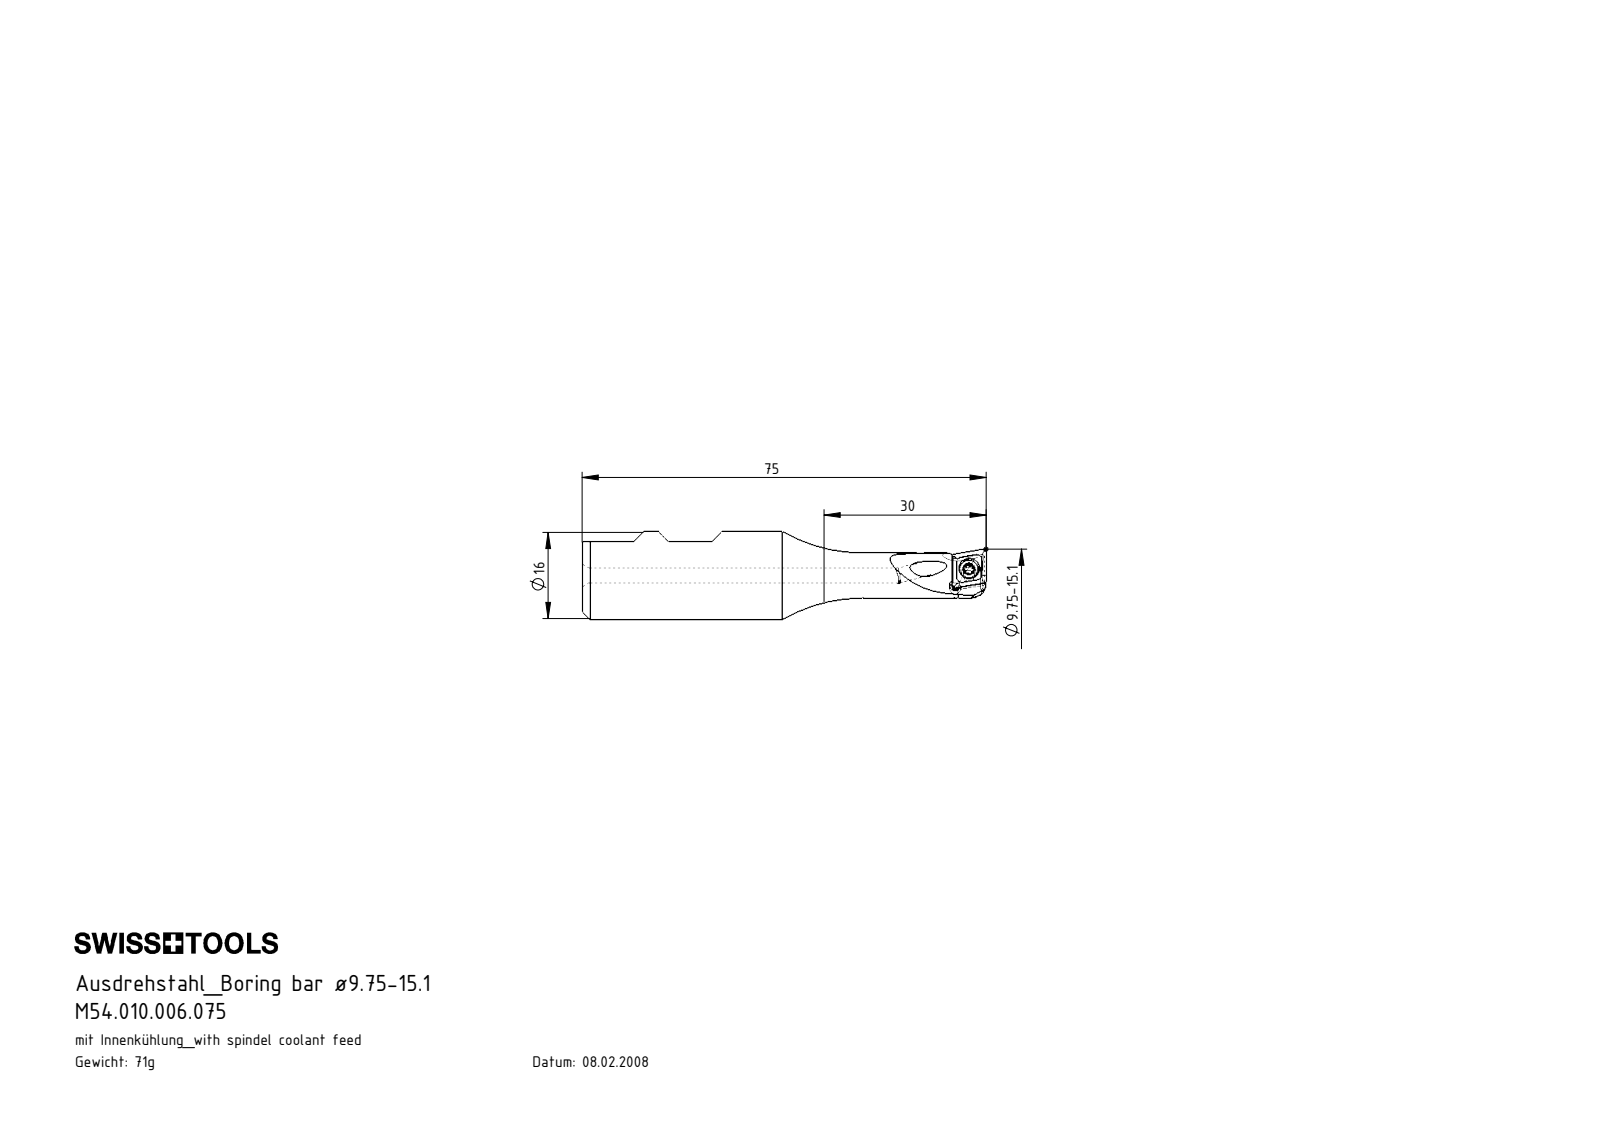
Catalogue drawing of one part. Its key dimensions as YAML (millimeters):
part_name: "WCA-ER2.001.005_A; B10.WCA.K11.075; B10-WCA.K11.075_C; CCMT060204"
step_written_by: "SolidWorks 2017 (AUTOMOTIVE_DESIGN)"
units: millimeters
bodies: {solids: 3, faces: 107, planar: 34, cylindrical: 29, other: 44}
overall_size: [75, 16, 16]
volume: 9033
surface_area: 3915
round_holes:
  - {diameter: 3, count: 2}
  - {diameter: 2.05, count: 1}
  - {diameter: 2.1, count: 1}
  - {diameter: 2.8, count: 1}
  - {diameter: 3.85, count: 1}
round_bosses_or_shafts:
  - {diameter: 16, count: 1}
  - {diameter: 8.05, count: 1}
  - {diameter: 3.4, count: 1}
  - {diameter: 2.5, count: 1}
partial_cylinders:
  - {radius: 0.21, count: 6}
  - {radius: 0.36, count: 5}
  - {radius: 0.36, count: 1}
  - {radius: 1, count: 1}
  - {radius: 3.5, count: 1}
  - {radius: 4.1, count: 1}
  - {radius: 5, count: 1}
  - {radius: 7, count: 1}
face_to_face_distances: [2.28, 10.25, 2.38, 68.8, 1.48, 0.8, 0.9, 2.62, 4.1, 4.9]
hole_center_spacings: [3.99, 4.09]
